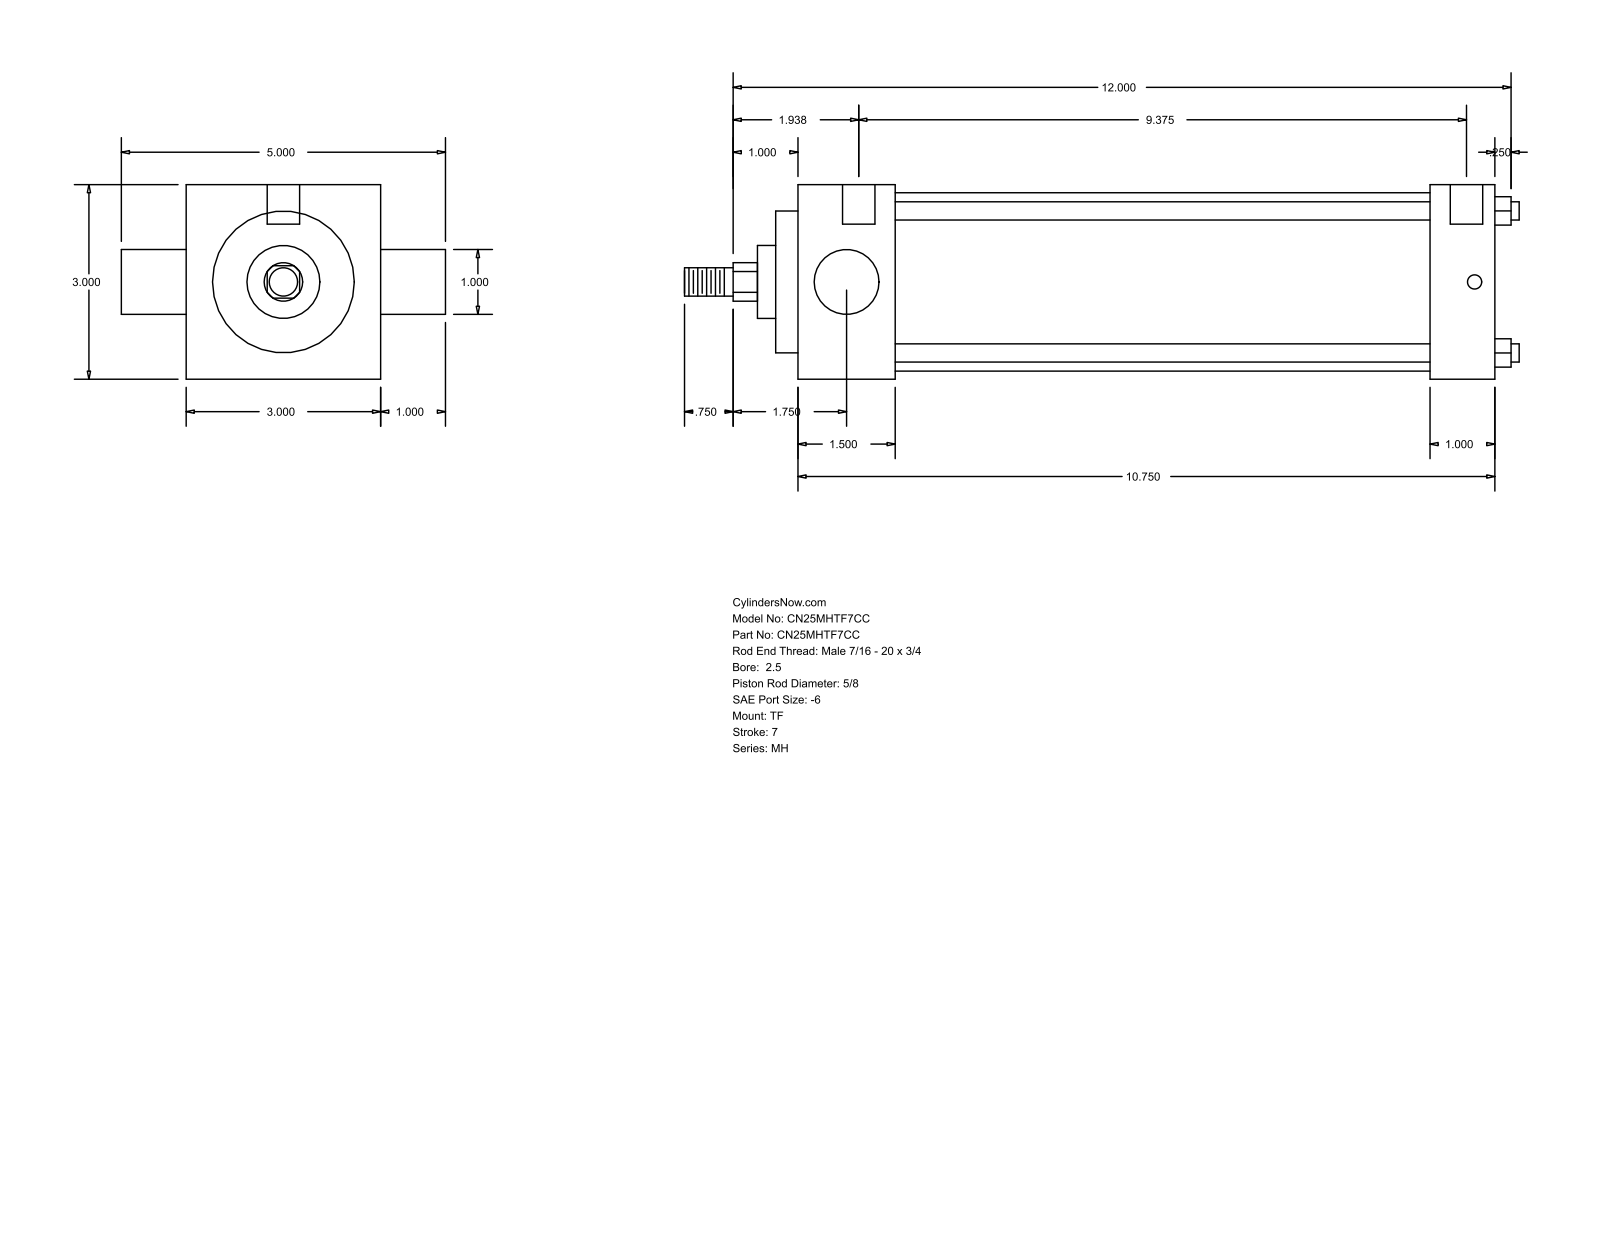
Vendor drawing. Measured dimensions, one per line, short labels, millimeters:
name: MH_TF__0250_0.625
written by: GSSL Pune (CONFIG_CONTROL_DESIGN)
unit: mm
bodies: 0 solids, 86 faces (61 planar, 25 cylindrical, 0 other)
size: 327.02 × 127 × 76.2
holes: 3× ⌀5.56, 2× ⌀12.7
bosses: 4× ⌀7.14, 1× ⌀69.85, 1× ⌀55.55, 1× ⌀28.57, 1× ⌀25.4, 1× ⌀15.88, 1× ⌀11.11
rounds: 1× R7.54
face distances: 76.2, 273.05, 25.4, 38.1, 234.95, 247.65, 209.55, 8.73, 46.83, 256.38
hole spacings: 3.17, 4.76, 238.13, 241.3, 242.89, 246.06
